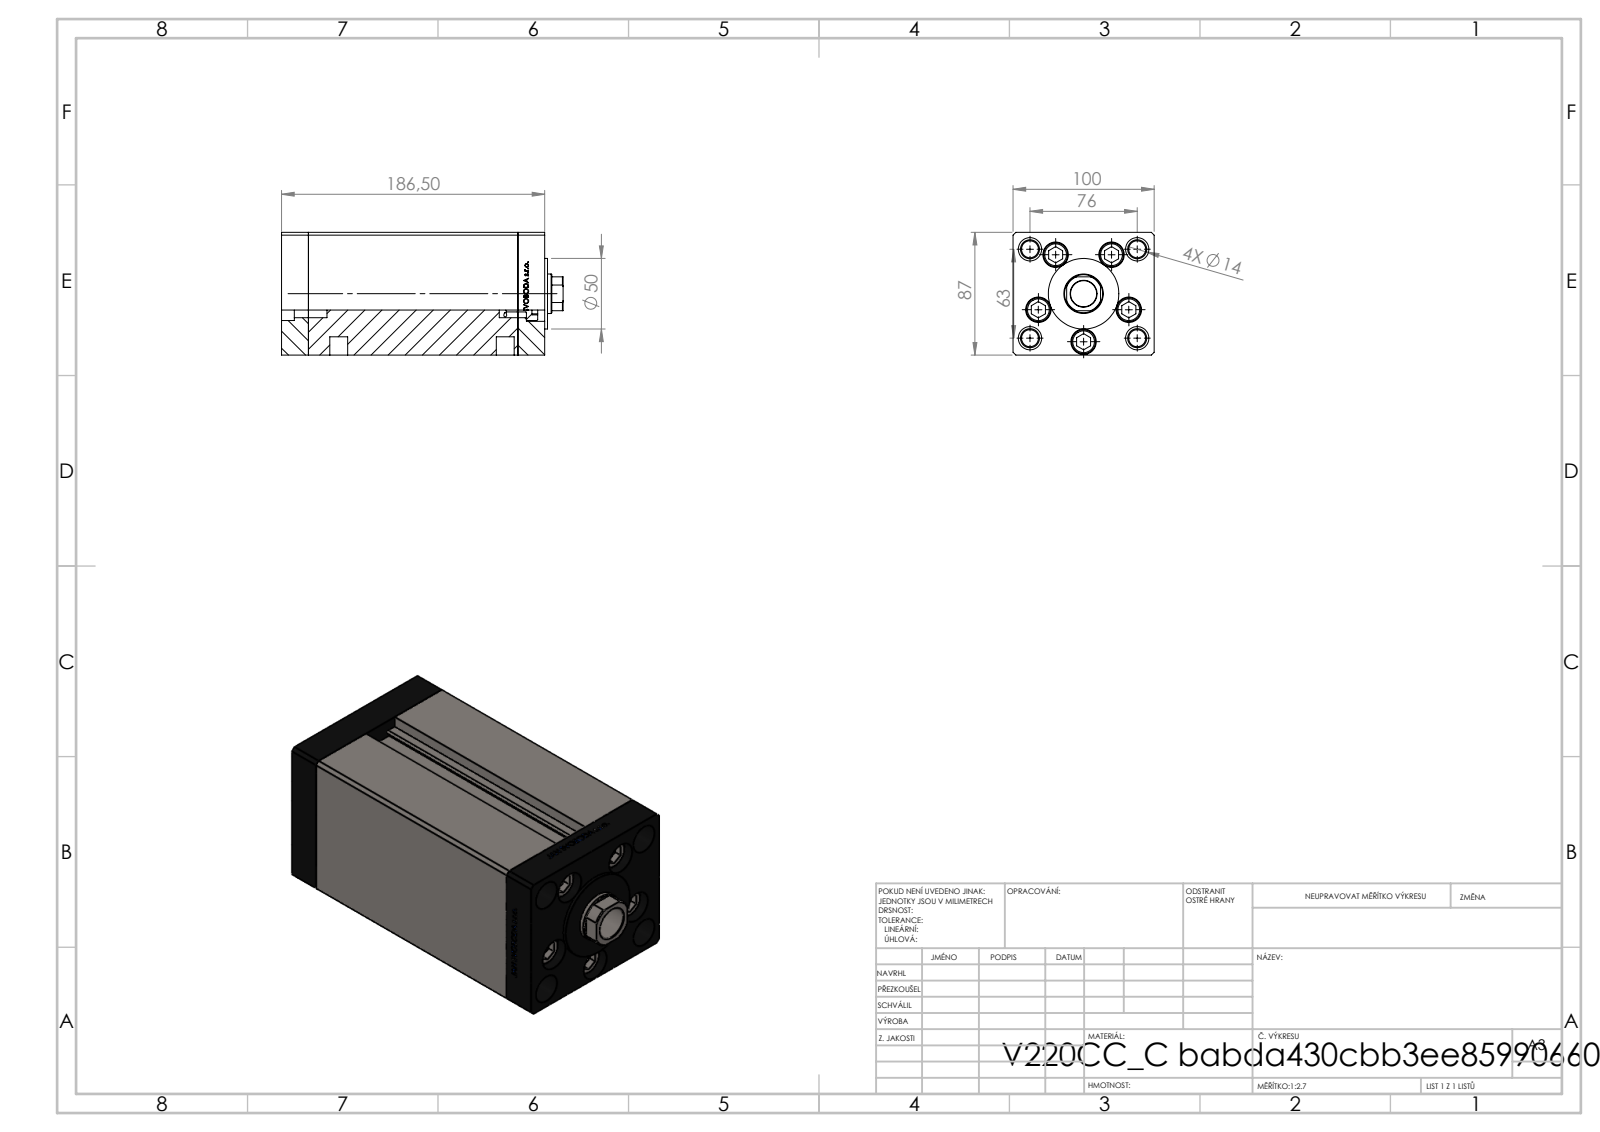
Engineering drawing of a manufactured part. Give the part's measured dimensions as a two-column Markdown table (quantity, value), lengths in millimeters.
| quantity | value |
| --- | --- |
| part name | ALLEN BOLT; V220C FRONT; V220C_C MIDDLE; V220C BACK_C (+1 more) |
| STEP written by | SolidWorks 2019 (CONFIG_CONTROL_DESIGN) |
| units | millimeters |
| bodies | 13 solids, 1182 faces (544 planar, 176 cylindrical, 462 other) |
| overall size | 199.5 × 100 × 87 |
| volume | 1 328 000 mm³ |
| surface area | 230 838 mm² |
| round holes (diameter × count) | 13.5 × 9, 18 × 5, 2 × 4, 12 × 4, 13.16 × 4, 16.5 × 4, 17 × 1, 18.5 × 1, 28 × 1 |
| round bosses / shafts (diameter × count) | 8 × 5, 17 × 4, 50 × 1 |
| partial cylindrical surfaces (radius × count) | 0.93 × 2, 13.5 × 1 |
| main face-to-face distances | 100, 87, 19, 148.5, 167.5, 34.25, 186.5, 152.25, 133.25, 15.25 |
| hole center spacings | 34, 49.36, 18.59, 21.03, 38.08, 39.27, 40.83, 43.24 |
